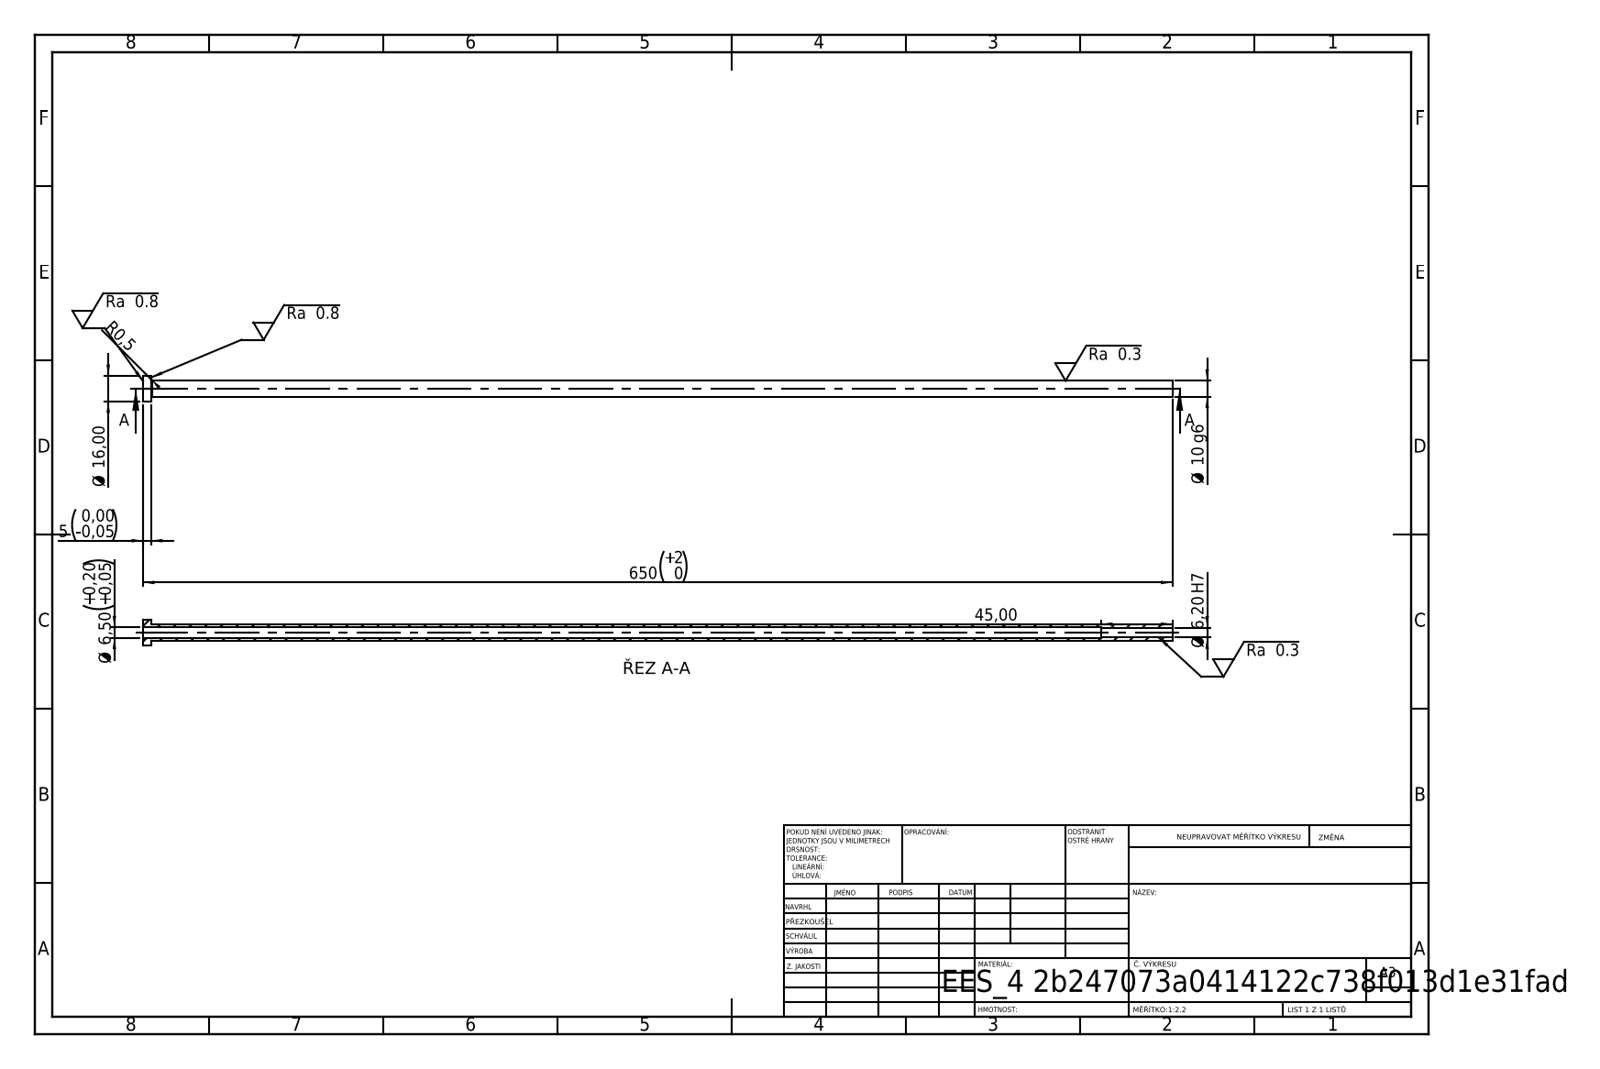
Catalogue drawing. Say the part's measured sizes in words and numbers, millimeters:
Its 3-D file was written by "SolidWorks 2019 (CONFIG_CONTROL_DESIGN)". It is 1 solid with 14 faces: 4 planar, 8 cylindrical and 2 other. Overall it measures 650 by 16 by 16 millimeters. Its volume is 30 231 cubic millimeters and its surface area 34 081 square millimeters. Round holes: 1 of diameter 6.2, 1 of diameter 6.5. Round bosses or shafts: 1 of diameter 16, 1 of diameter 10. The main face-to-face distances are 5, 650, 645, 605, 600, 45.
